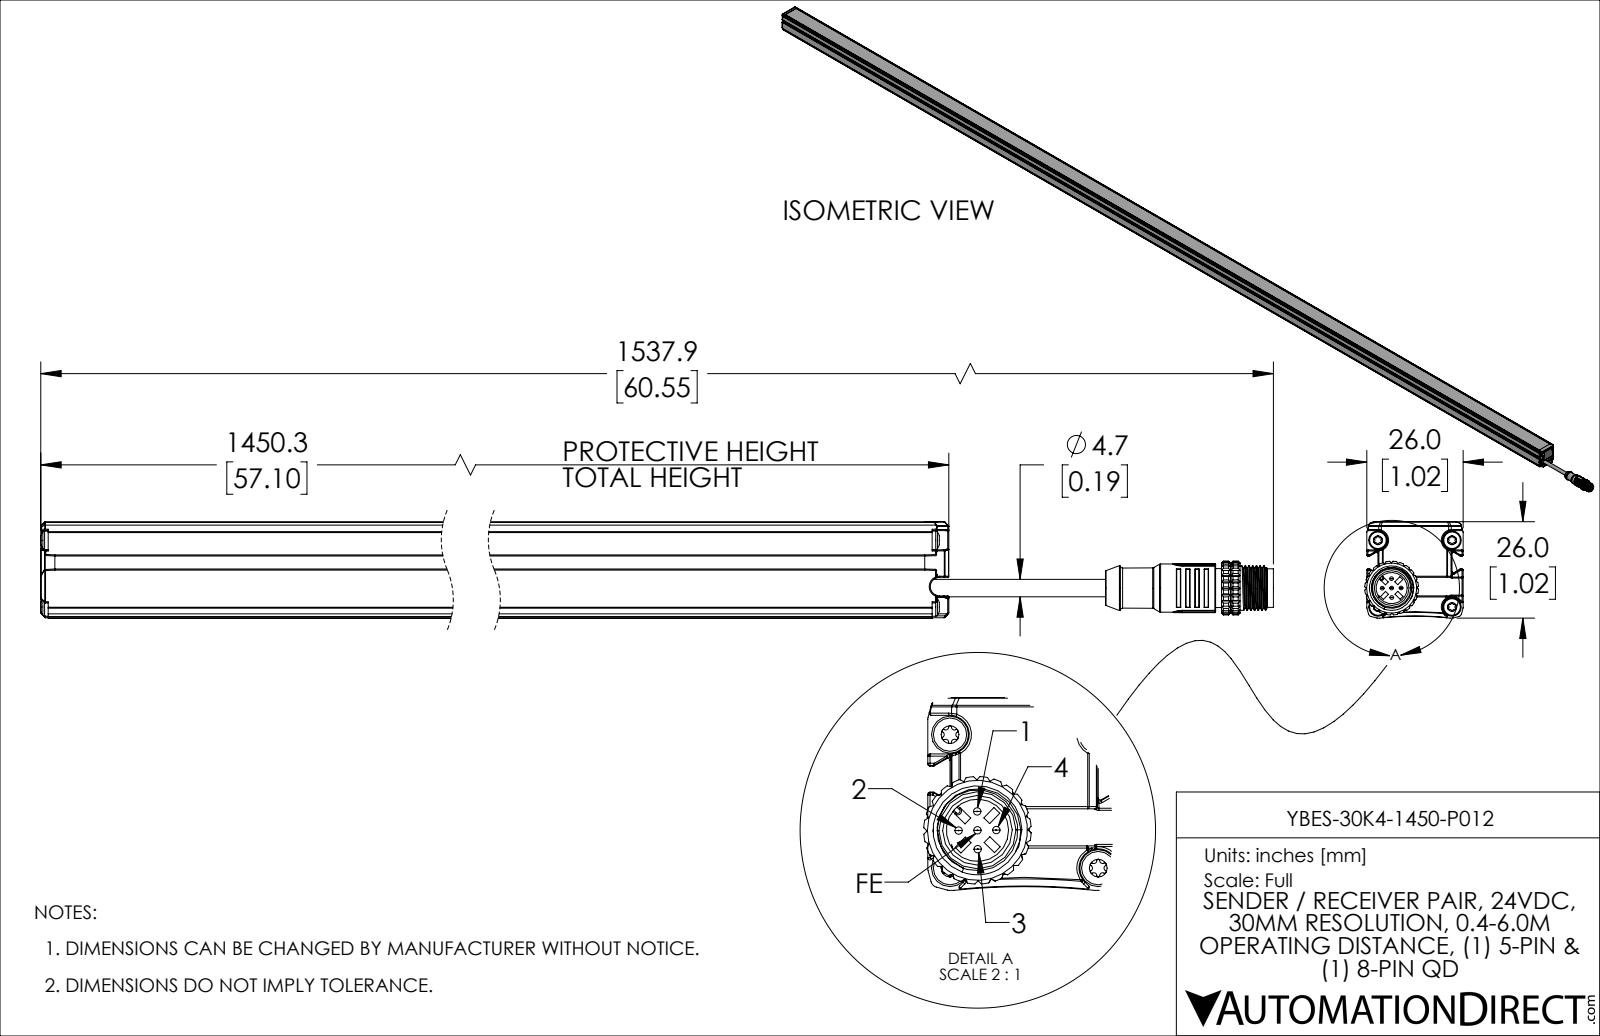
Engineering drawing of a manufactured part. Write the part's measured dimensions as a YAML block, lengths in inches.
part_name: "YBES-30K4-1450-P012"
step_written_by: "SolidWorks 2019 (AUTOMOTIVE_DESIGN)"
units: inches
bodies: {solids: 3, faces: 1373, planar: 438, cylindrical: 542, other: 393}
overall_size: [60.547, 1.045, 1.027]
volume: 56.72
surface_area: 273.8
round_holes:
  - {diameter: 0.094, count: 4}
  - {diameter: 0.1, count: 1}
  - {diameter: 0.146, count: 1}
  - {diameter: 0.331, count: 1}
round_bosses_or_shafts:
  - {diameter: 0.039, count: 5}
  - {diameter: 0.197, count: 4}
  - {diameter: 0.531, count: 1}
  - {diameter: 0.512, count: 1}
  - {diameter: 0.472, count: 1}
  - {diameter: 0.413, count: 1}
  - {diameter: 0.409, count: 1}
  - {diameter: 0.185, count: 1}
partial_cylinders:
  - {radius: 0.012, count: 110}
  - {radius: 0.008, count: 67}
  - {radius: 0.008, count: 24}
  - {radius: 0.015, count: 24}
  - {radius: 0.039, count: 18}
  - {radius: 0.006, count: 14}
  - {radius: 0.006, count: 6}
  - {radius: 0.098, count: 6}
face_to_face_distances: [1.024, 0.118, 0.906, 0.787, 0.597, 1.198, 1.208, 56.705, 0.135, 0.659]
hole_center_spacings: [0.709, 0.787, 1.059, 0.248, 0.528, 0.672, 0.819]
